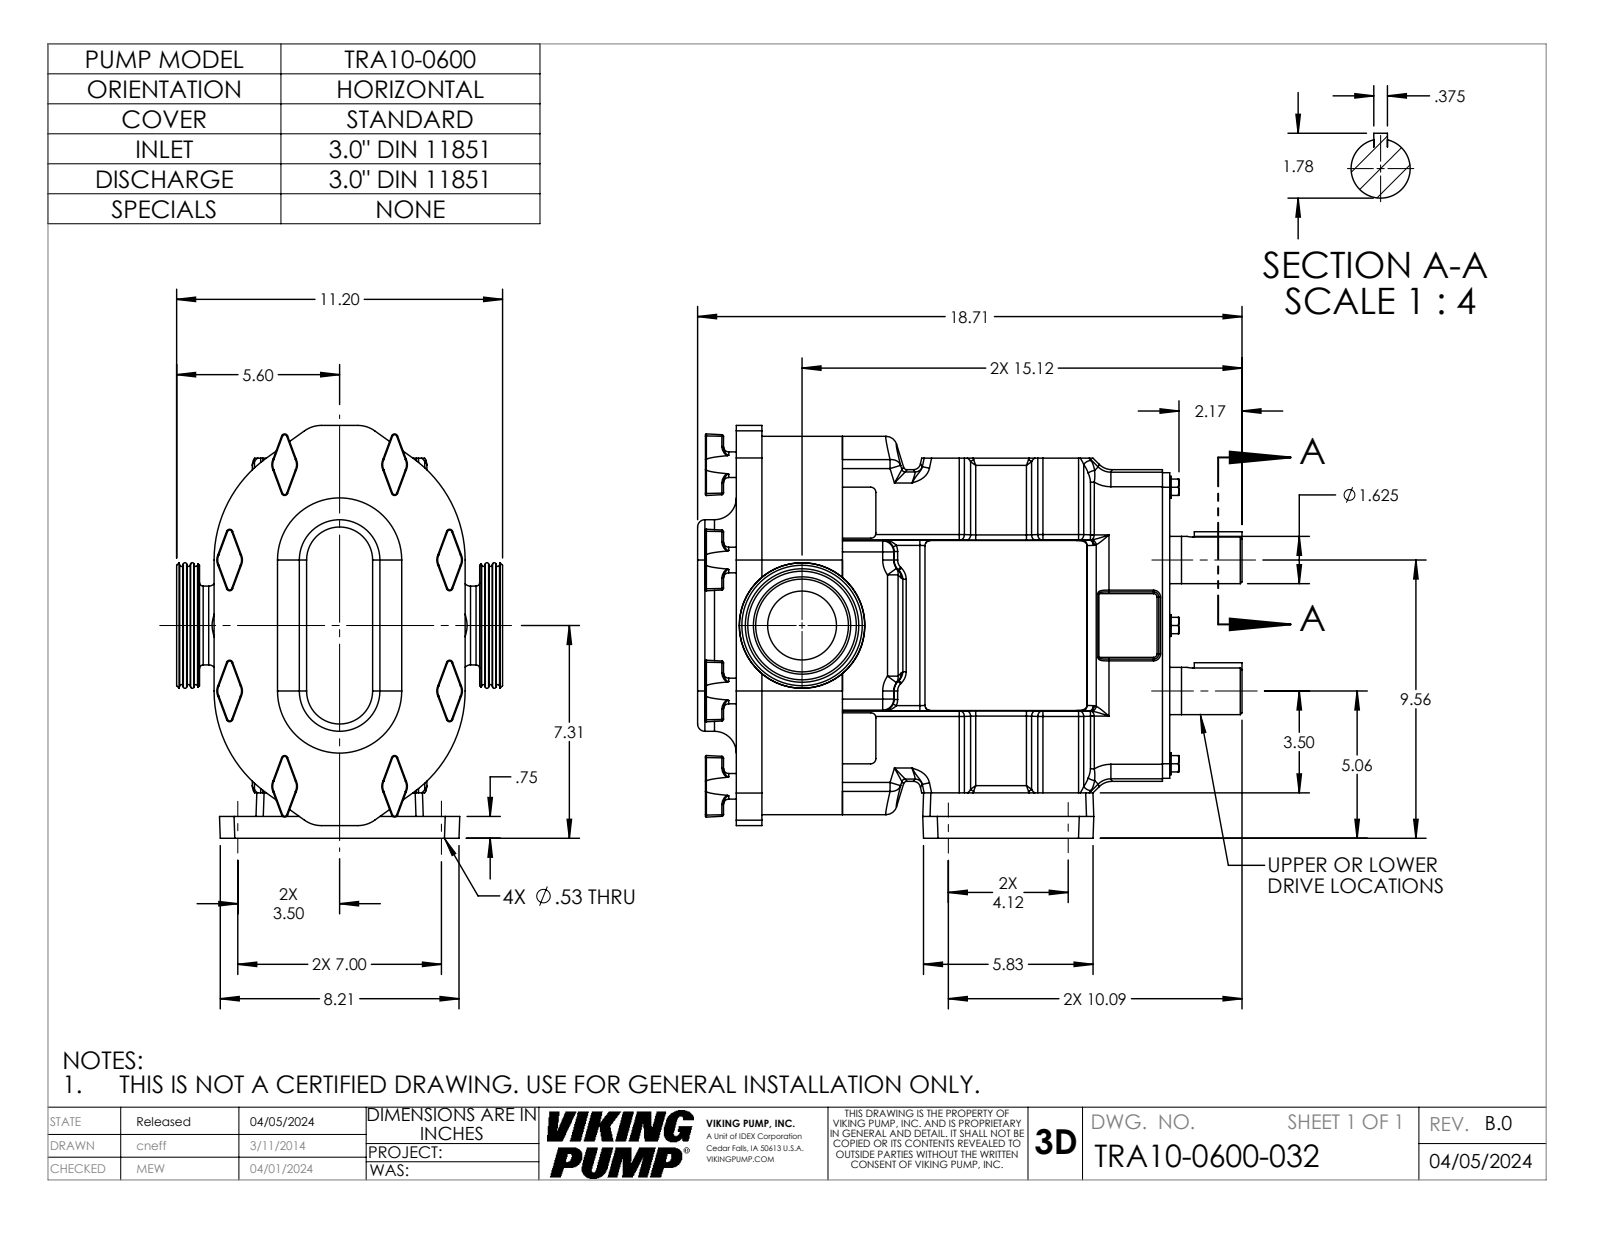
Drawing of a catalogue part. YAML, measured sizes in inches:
part_name: "TRA10-0600-GEARBOX-H; 0600DIN11851-30; TRA10-0600-032; TRA10-0600-COVER-STD (+1 more)"
step_written_by: "SolidWorks 2022 (AUTOMOTIVE_DESIGN)"
units: inches
bodies: {solids: 5, faces: 1109, planar: 289, cylindrical: 372, other: 448}
overall_size: [18.714, 14.185, 11.204]
volume: 1191
surface_area: 1393
round_holes:
  - {diameter: 0.531, count: 4}
  - {diameter: 2.368, count: 1}
  - {diameter: 3.732, count: 1}
round_bosses_or_shafts:
  - {diameter: 0.88, count: 8}
  - {diameter: 0.75, count: 6}
  - {diameter: 1.624, count: 2}
  - {diameter: 3.346, count: 1}
  - {diameter: 2.708, count: 1}
partial_cylinders:
  - {radius: 0.18, count: 44}
  - {radius: 0.06, count: 43}
  - {radius: 0.03, count: 32}
  - {radius: 0.25, count: 32}
  - {radius: 0.38, count: 28}
  - {radius: 0.12, count: 24}
  - {radius: 0.5, count: 20}
  - {radius: 0.375, count: 12}
face_to_face_distances: [2.769, 0.5, 0.88, 3.649, 0.36, 14.899, 14.019, 11.25, 6.5, 0.86]
hole_center_spacings: [4.12, 7, 8.122]
